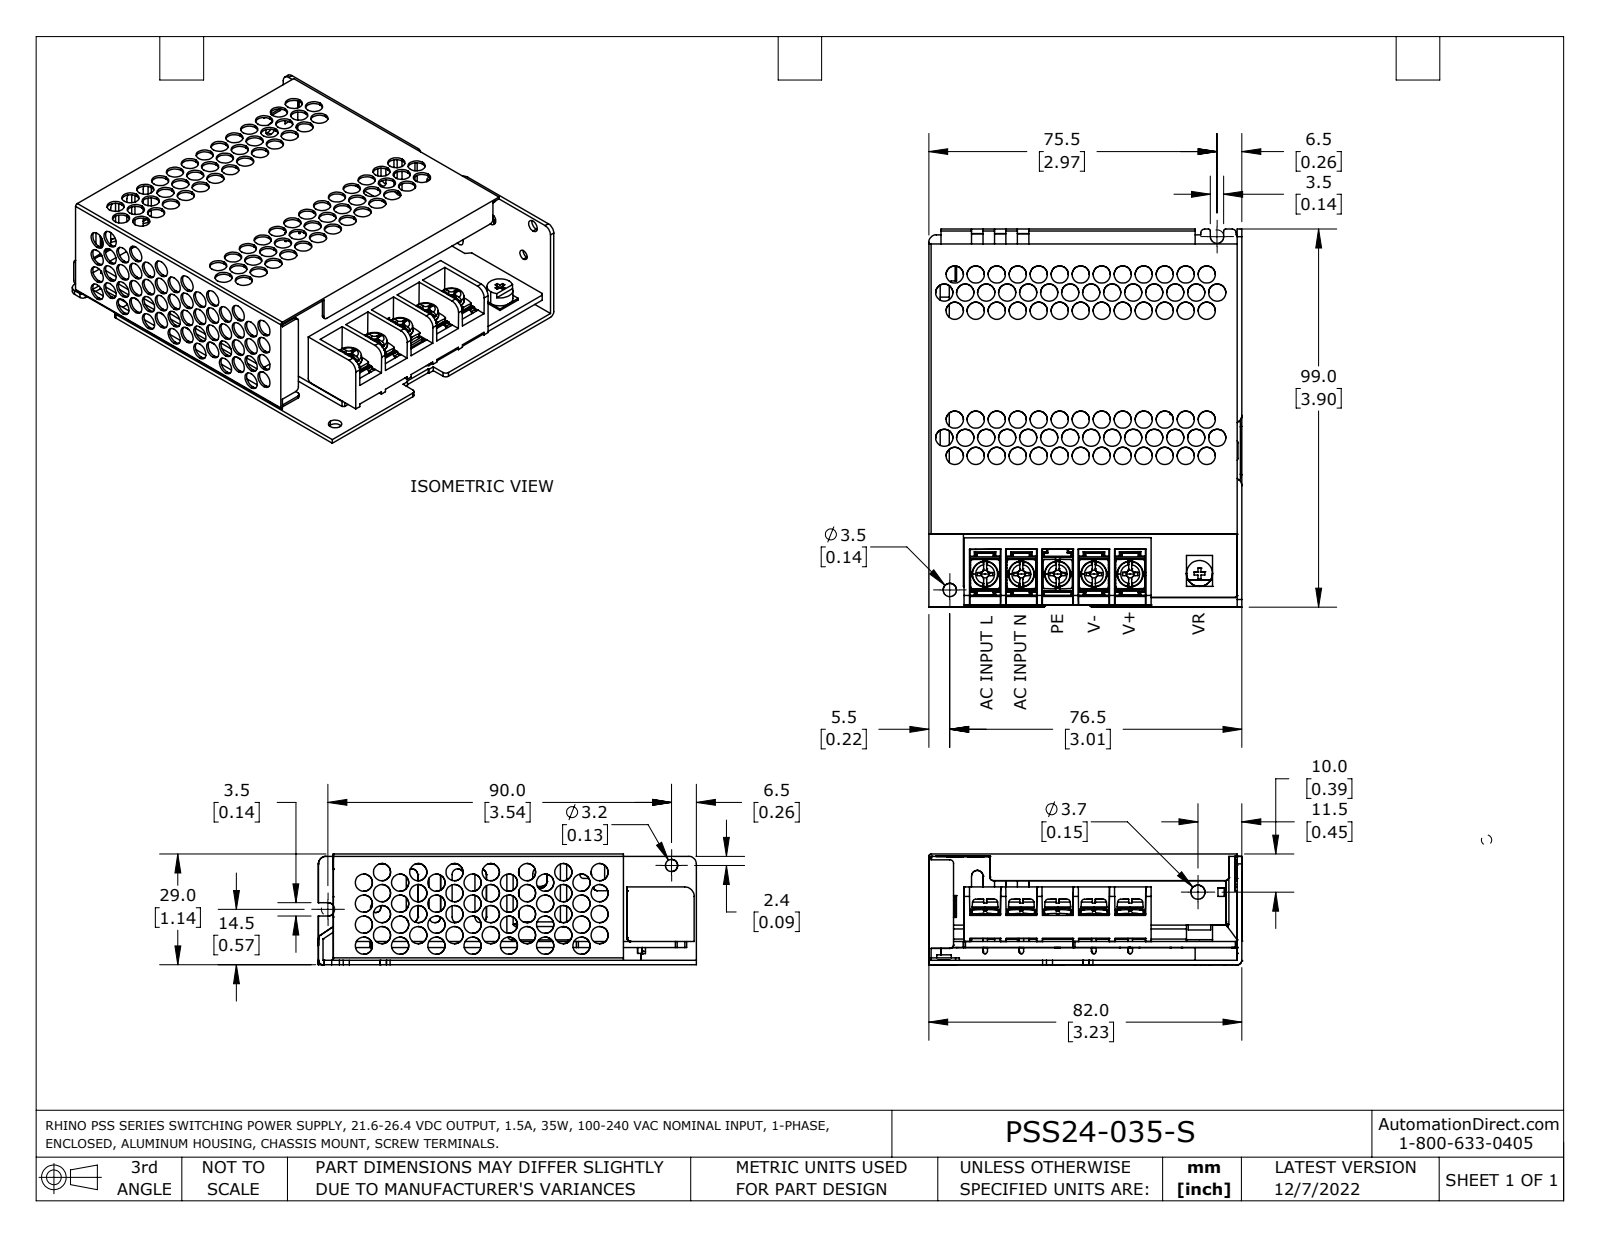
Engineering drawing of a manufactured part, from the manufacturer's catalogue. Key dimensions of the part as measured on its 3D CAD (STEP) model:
Part name (STEP PRODUCT): PSS12-035-S
STEP written by: SolidWorks 2021 (AUTOMOTIVE_DESIGN)
Units: inches
Bodies: 9 solids, 2079 faces (1098 planar, 682 cylindrical, 299 other)
Overall size (bounding box): 3.898 × 3.228 × 1.142
Volume: 2.123 in³ · Surface area: 99.61 in²
Round holes (diameter × count): ⌀0.177 ×136, ⌀0.126 ×6, ⌀0.138 ×6, ⌀0.106 ×4, ⌀0.016 ×2, ⌀0.02 ×2, ⌀0.022 ×2, ⌀0.069 ×1, ⌀0.102 ×1, ⌀0.146 ×1, ⌀0.224 ×1
Round bosses / shafts (diameter × count): ⌀0.165 ×4, ⌀0.268 ×1, ⌀0.217 ×1, ⌀0.15 ×1
Partial cylindrical surfaces — rounded edges, fillets, slot ends (radius × count): R0.039 ×58, R0.006 ×56, R0.016 ×36, R0.008 ×26, R0.059 ×14, R0.02 ×13, R0.004 ×8, R0.012 ×8
Main face-to-face distances: 0.047, 0.177, 0.024, 0.13, 0.24, 0.063, 0.193, 1.071, 1.118, 0.941
Hole centre spacings: 0.217, 0.216, 0.432, 0.375, 0.433, 0.374, 0.779, 0.572
